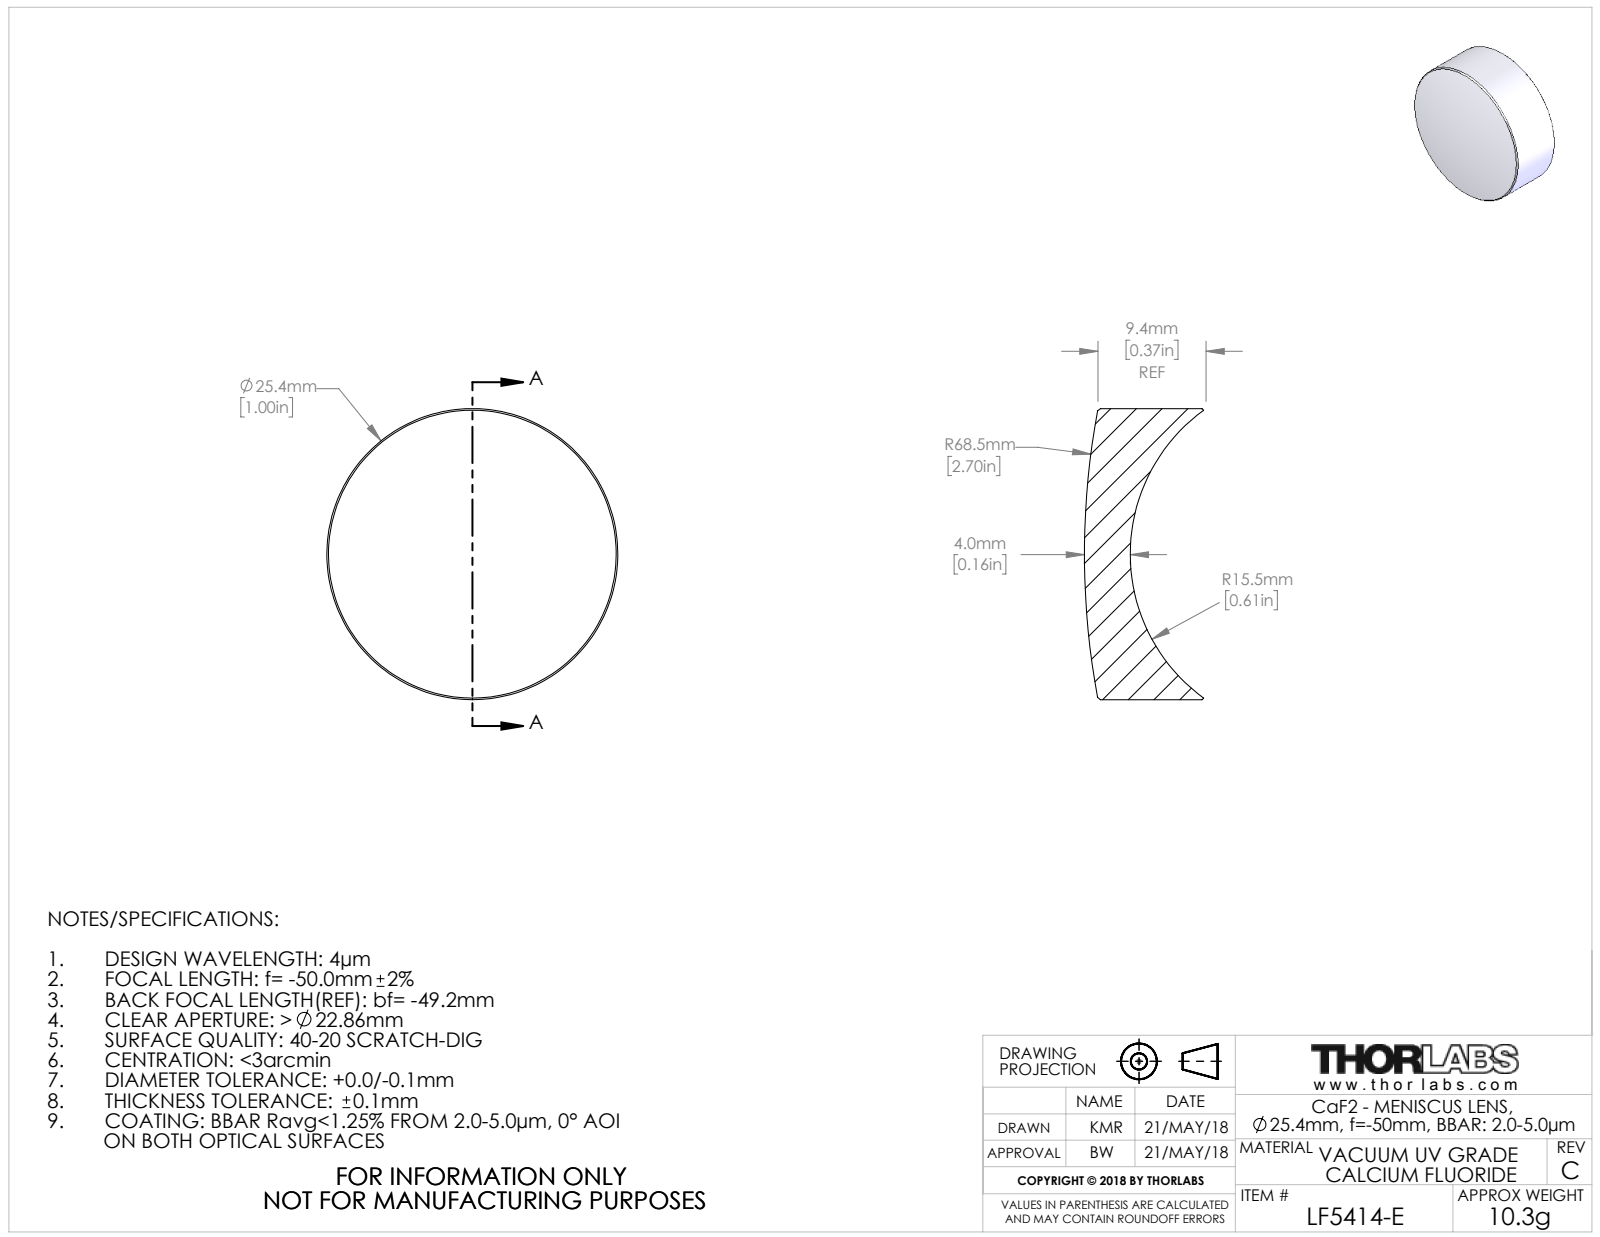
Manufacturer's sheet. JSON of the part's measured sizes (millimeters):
{"part_name": "20173-E0W", "step_written_by": "SolidWorks 2016 (CONFIG_CONTROL_DESIGN)", "units": "millimeters", "bodies": {"solids": 1, "faces": 10, "planar": 0, "cylindrical": 2, "other": 8}, "overall_size": [25.4, 25.4, 10.4], "volume_mm3": 3240, "surface_area_mm2": 1870, "round_bosses_or_shafts": [[25.4, 1]]}
